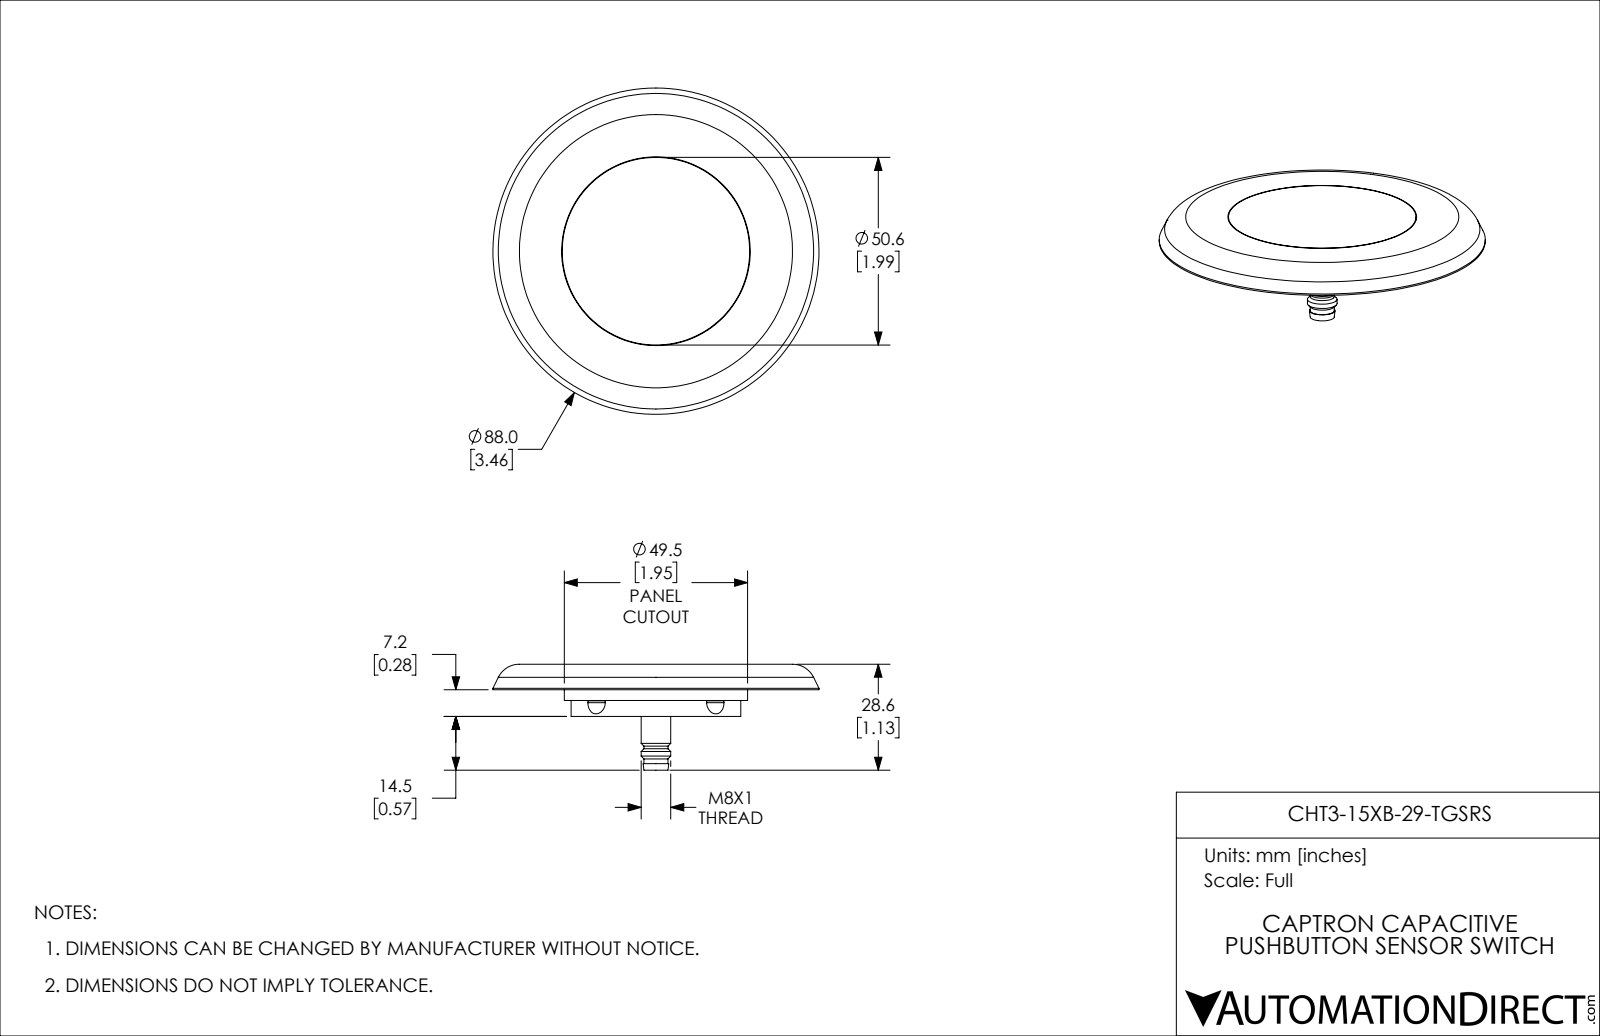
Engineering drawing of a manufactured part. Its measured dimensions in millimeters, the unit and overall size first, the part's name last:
Units: millimetres
Overall size (bounding box): 88 × 88 × 28.6
Round holes (diameter × count): ⌀46.1 ×1, ⌀50.9 ×1
Round bosses / shafts (diameter × count): ⌀1 ×5, ⌀50.6 ×1, ⌀49.5 ×1, ⌀45.8 ×1, ⌀8 ×1, ⌀6.5 ×1
Partial cylindrical surfaces — rounded edges, fillets, slot ends (radius × count): R5 ×4, R0.5 ×2, R0.9 ×1, R1 ×1, R2.9 ×1
Main face-to-face distances: 6.9, 4.6, 2.3, 7.2, 11.8, 14.1, 0.5, 4.3, 7.7, 2.9
Volume: 49 980 mm³ · Surface area: 21 720 mm²
Bodies: 10 solids, 90 faces (25 planar, 40 cylindrical, 25 other)
Part name (STEP PRODUCT): CHT3-15XB-29-TGSRS
STEP written by: SolidWorks 2019 (CONFIG_CONTROL_DESIGN)
